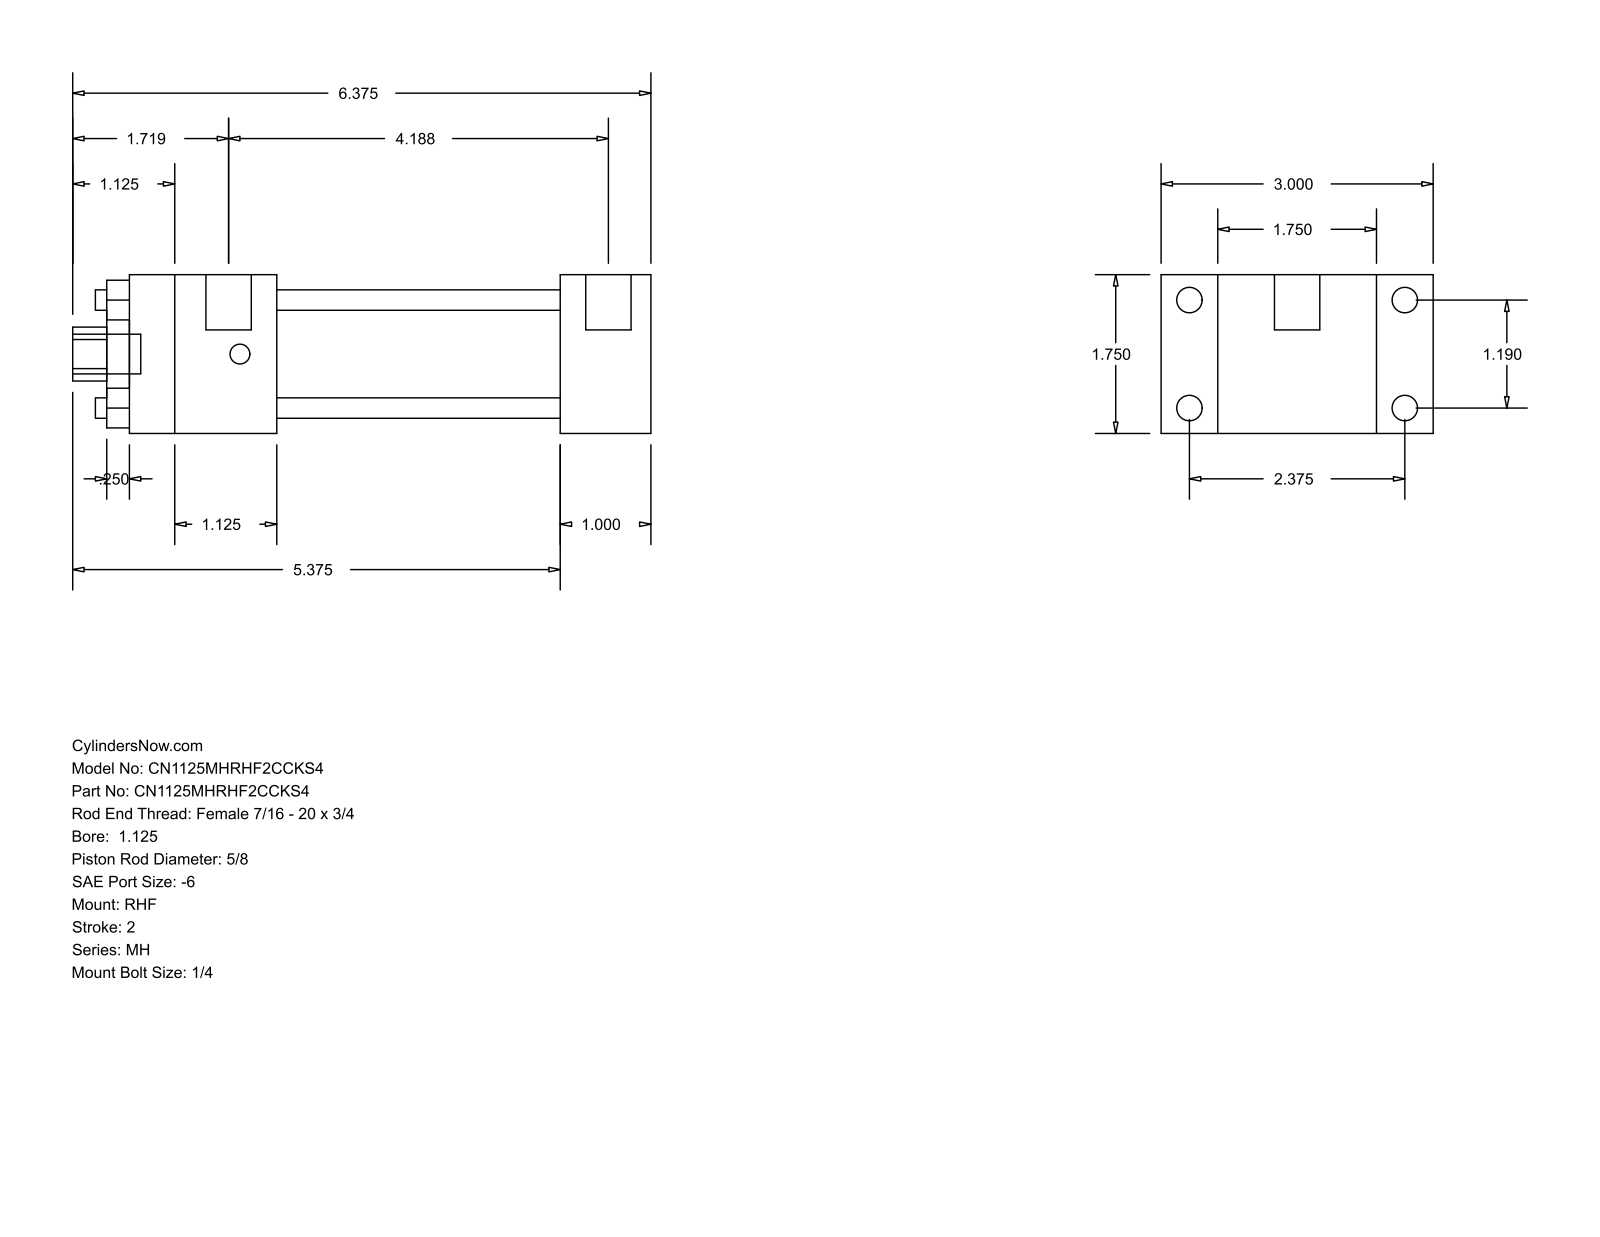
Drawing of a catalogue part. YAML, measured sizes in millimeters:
part_name: "MH_RHF__0112_0.625"
step_written_by: "GSSL Pune (CONFIG_CONTROL_DESIGN)"
units: millimeters
bodies: {solids: 0, faces: 88, planar: 60, cylindrical: 28, other: 0}
overall_size: [161.93, 76.2, 44.45]
round_holes:
  - {diameter: 5.71, count: 4}
  - {diameter: 15.88, count: 1}
  - {diameter: 28.57, count: 1}
  - {diameter: 34.92, count: 1}
round_bosses_or_shafts:
  - {diameter: 7.14, count: 4}
  - {diameter: 5.56, count: 4}
  - {diameter: 12.7, count: 2}
  - {diameter: 11.11, count: 1}
partial_cylinders:
  - {radius: 7.54, count: 1}
face_to_face_distances: [44.46, 15.87, 60.33, 25.4, 76.2, 79.38, 104.78, 41.27, 120.65, 146.05]
hole_center_spacings: [21.37, 30.22, 42.74]
